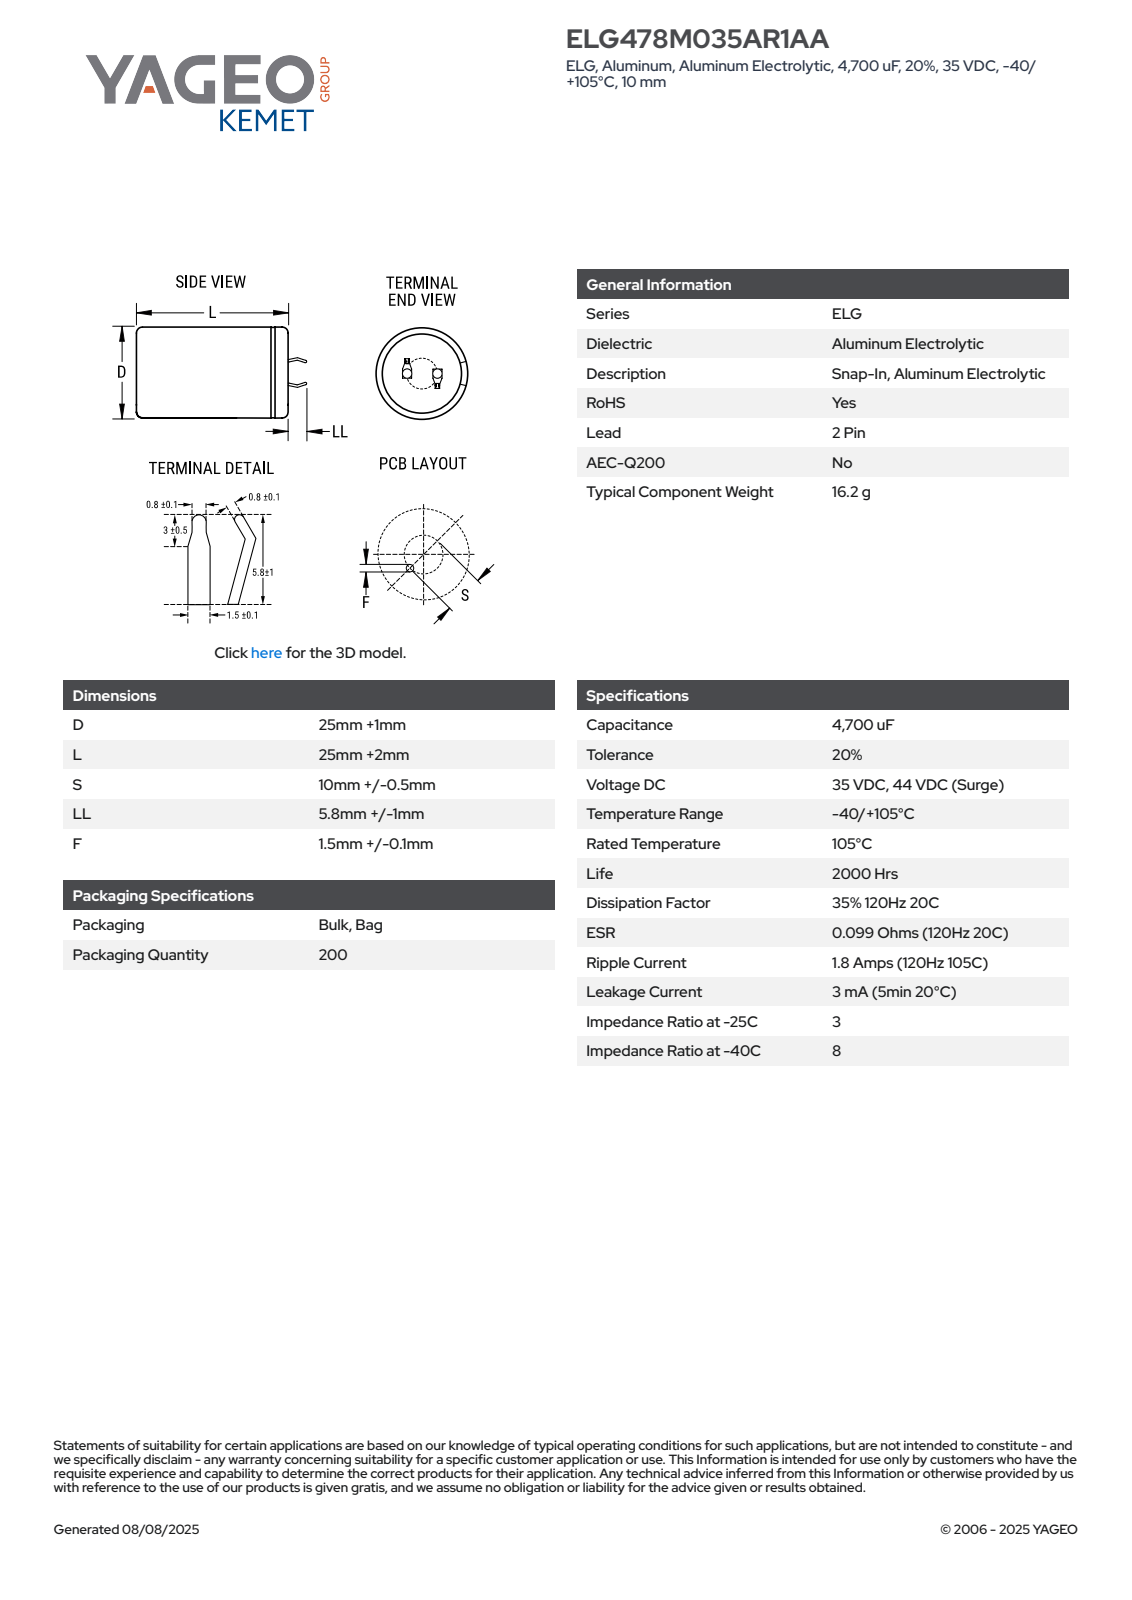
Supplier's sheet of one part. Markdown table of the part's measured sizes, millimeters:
| quantity | value |
| --- | --- |
| part name | CARS_K2P_25X25_D26L27S10LL6.8F1.6 |
| STEP written by | SolidWorks 2014 (AUTOMOTIVE_DESIGN) |
| units | millimeters |
| bodies | 1 solid, 100 faces (52 planar, 9 cylindrical, 39 other) |
| overall size | 33.79 × 26 × 26 |
| volume | 14 142 mm³ |
| surface area | 3 286 mm² |
| round holes (diameter × count) | 23 × 1 |
| round bosses / shafts (diameter × count) | 26 × 1 |
| partial cylindrical surfaces (radius × count) | 12.99 × 1 |
| main face-to-face distances | 26.99, 27.49, 0.5, 0.6, 7.08, 0.75, 1.35, 7.68, 6.48, 0.59 |
